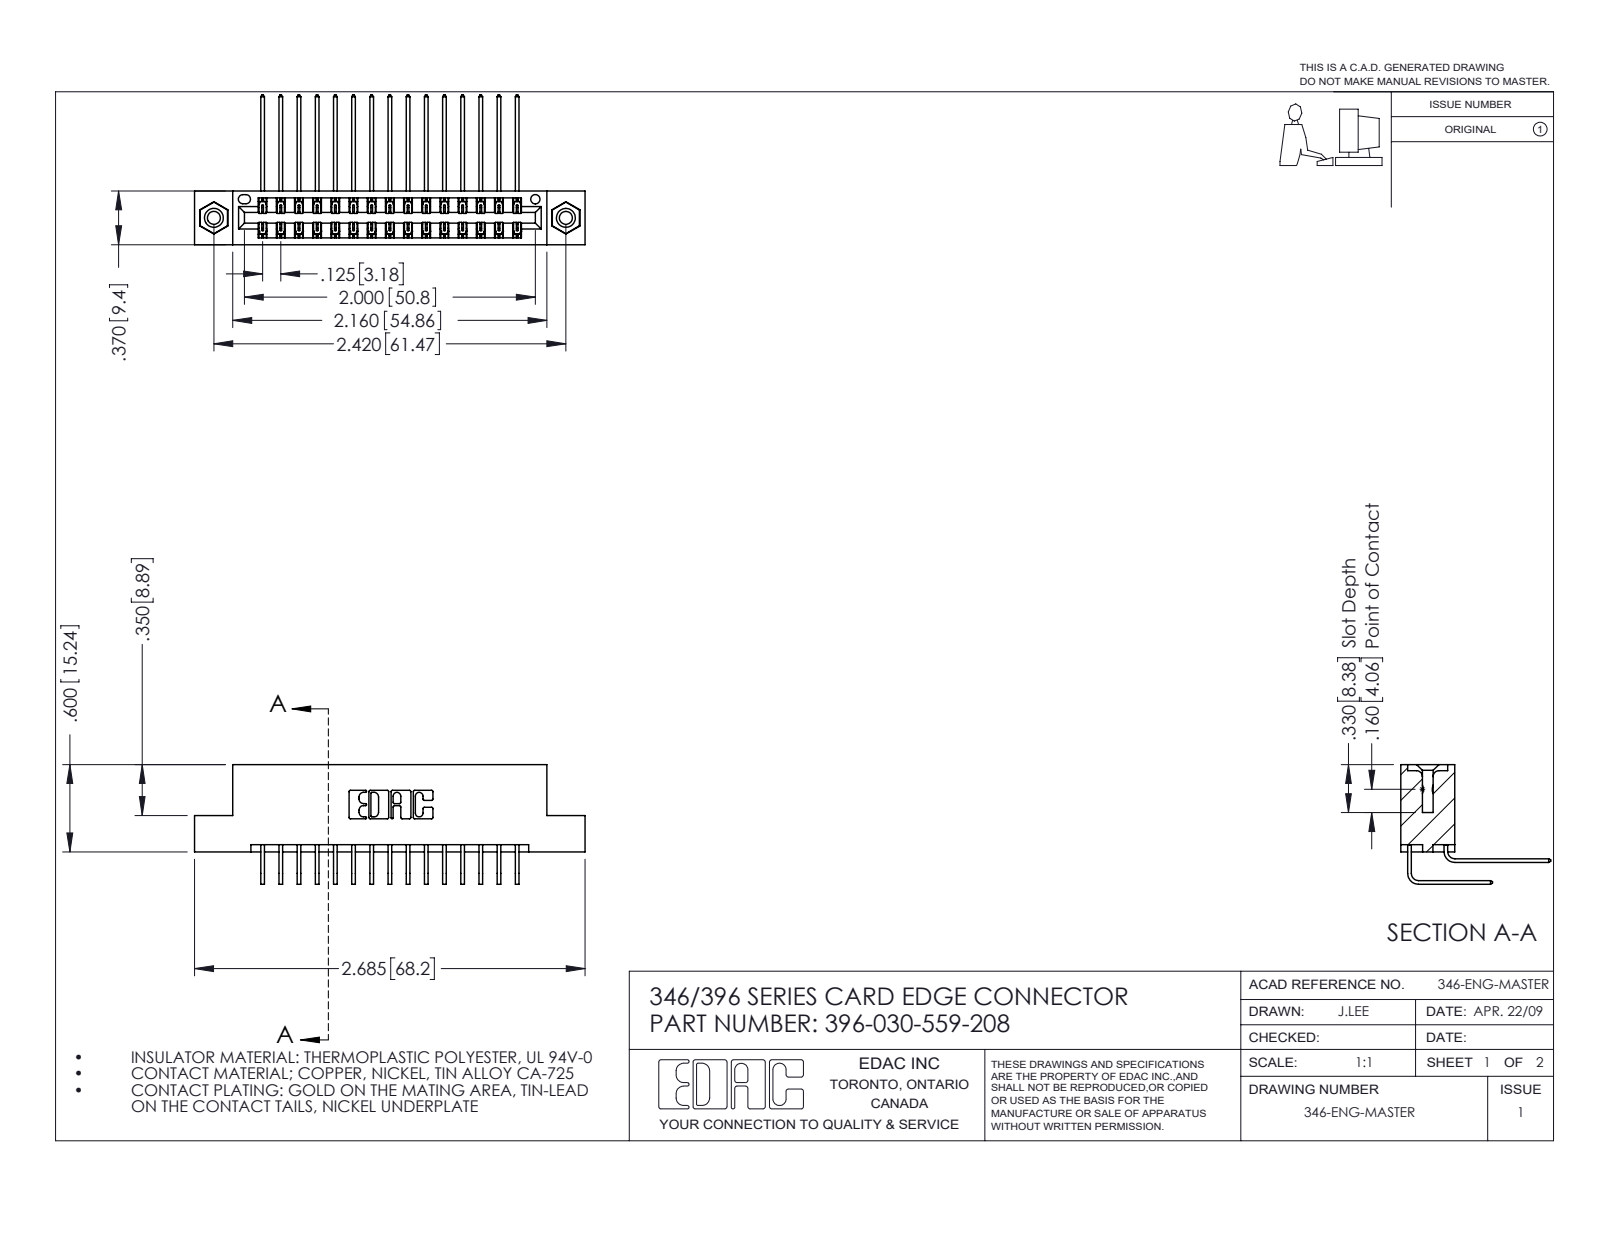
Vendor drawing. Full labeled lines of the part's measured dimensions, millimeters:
Part name (STEP PRODUCT): 345-292-001_558 559 Tail - 1; 345-250-001_345-250-003-102; 345-292-001_559 Tail - 2; 396-030-559-208 (+1 more)
STEP written by: SolidWorks 2016 (CONFIG_CONTROL_DESIGN)
Units: millimetres
Bodies: 33 solids, 1802 faces (1218 planar, 568 cylindrical, 16 other)
Overall size (bounding box): 68.2 × 26.2 × 20.9
Volume: 6 600 mm³ · Surface area: 9 510 mm²
Round holes (diameter × count): ⌀2.3 ×2, ⌀3.2 ×2, ⌀4 ×2, ⌀1.6 ×1
Round bosses / shafts (diameter × count): ⌀3.9 ×2
Partial cylindrical surfaces — rounded edges, fillets, slot ends (radius × count): R0.2 ×45, R0.3 ×22, R0.2 ×6, R0.8 ×6, R0.7 ×3, R0.4 ×2, R0.6 ×2, R0.6 ×2
Main face-to-face distances: 1.2, 8.2, 6.4, 0.6, 9.4, 1.8, 7.6, 7, 3.8, 5.6
Hole centre spacings: 6.2, 56.2, 61.5
